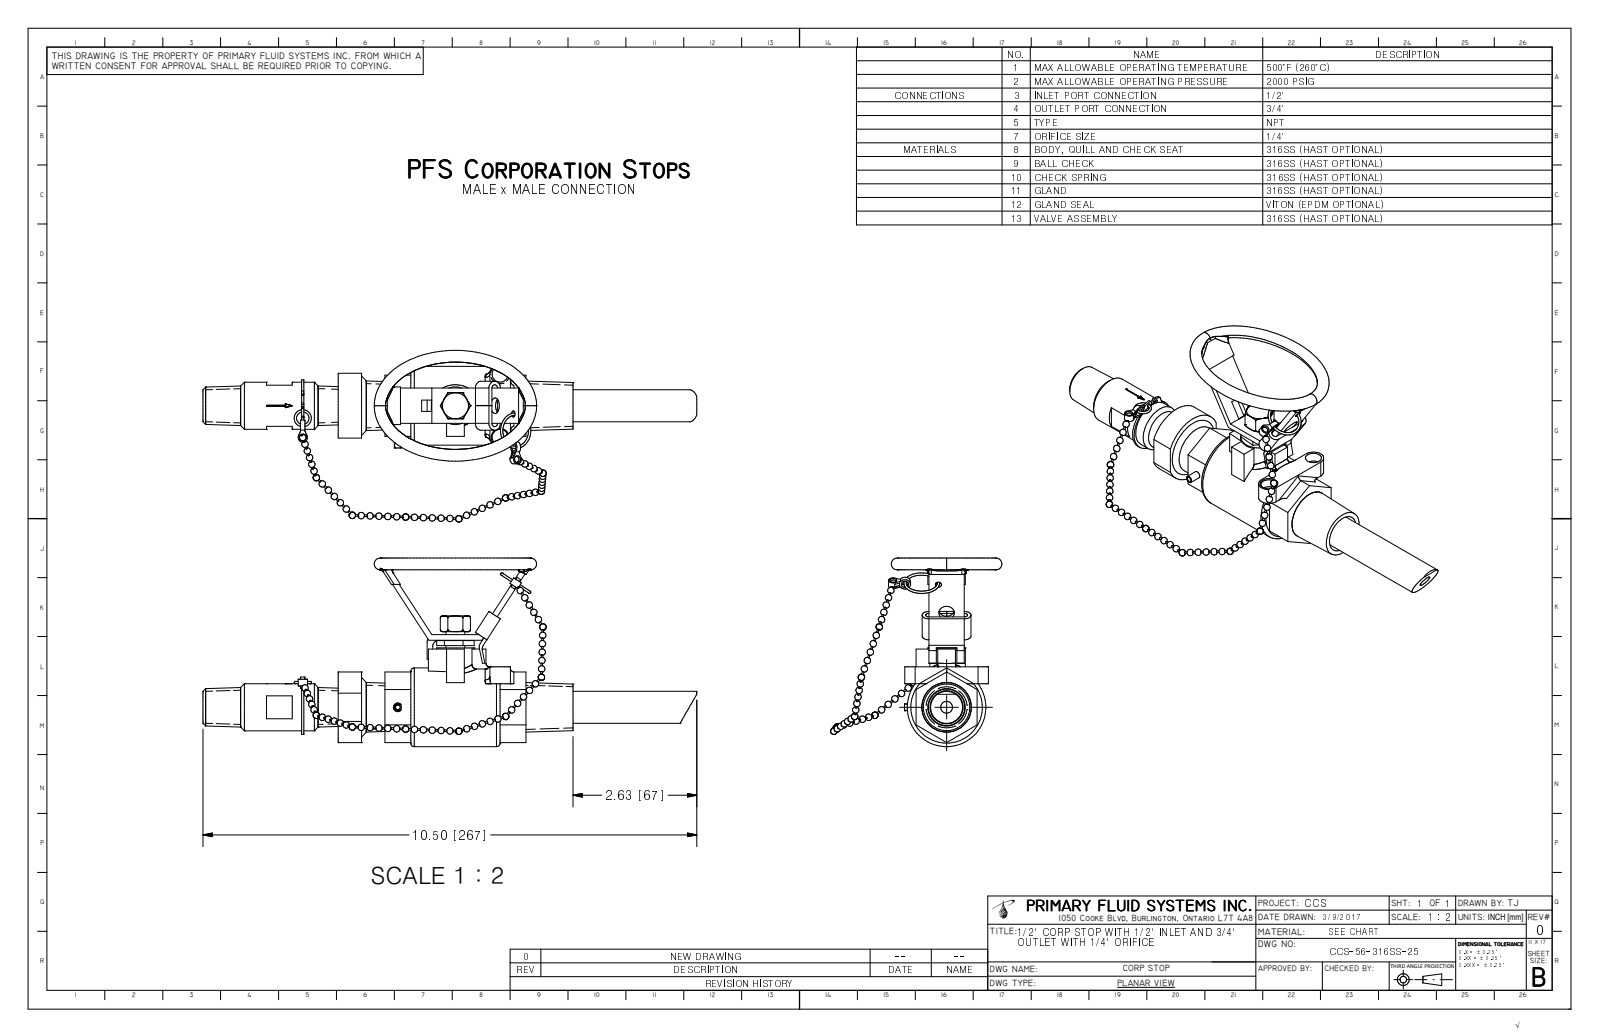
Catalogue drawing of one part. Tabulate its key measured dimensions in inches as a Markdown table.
| quantity | value |
| --- | --- |
| part name | CCS-56-316SS-25_R0 |
| STEP written by | Autodesk Inventor 2009 (AUTOMOTIVE_DESIGN) |
| units | inches |
| bodies | 0 solids, 390 faces (178 planar, 41 cylindrical, 171 other) |
| overall size | 10.5 × 4 × 3.64 |
| round holes (diameter × count) | 0.079 × 1, 0.25 × 1, 0.469 × 1 |
| round bosses / shafts (diameter × count) | 1.67 × 1, 1.094 × 1, 1 × 1, 0.8 × 1, 0.679 × 1, 0.4 × 1, 0.15 × 1 |
| partial cylindrical surfaces (radius × count) | 0.075 × 4, 0.043 × 2, 0.05 × 2, 0.145 × 2, 0.15 × 2, 0.157 × 2, 0.125 × 1, 0.165 × 1 |
| main face-to-face distances | 1.299, 0.12, 0.55, 0.275, 1.025, 0.12, 0.993, 0.16, 2.45, 0.038 |
| hole center spacings | 0.535 |
